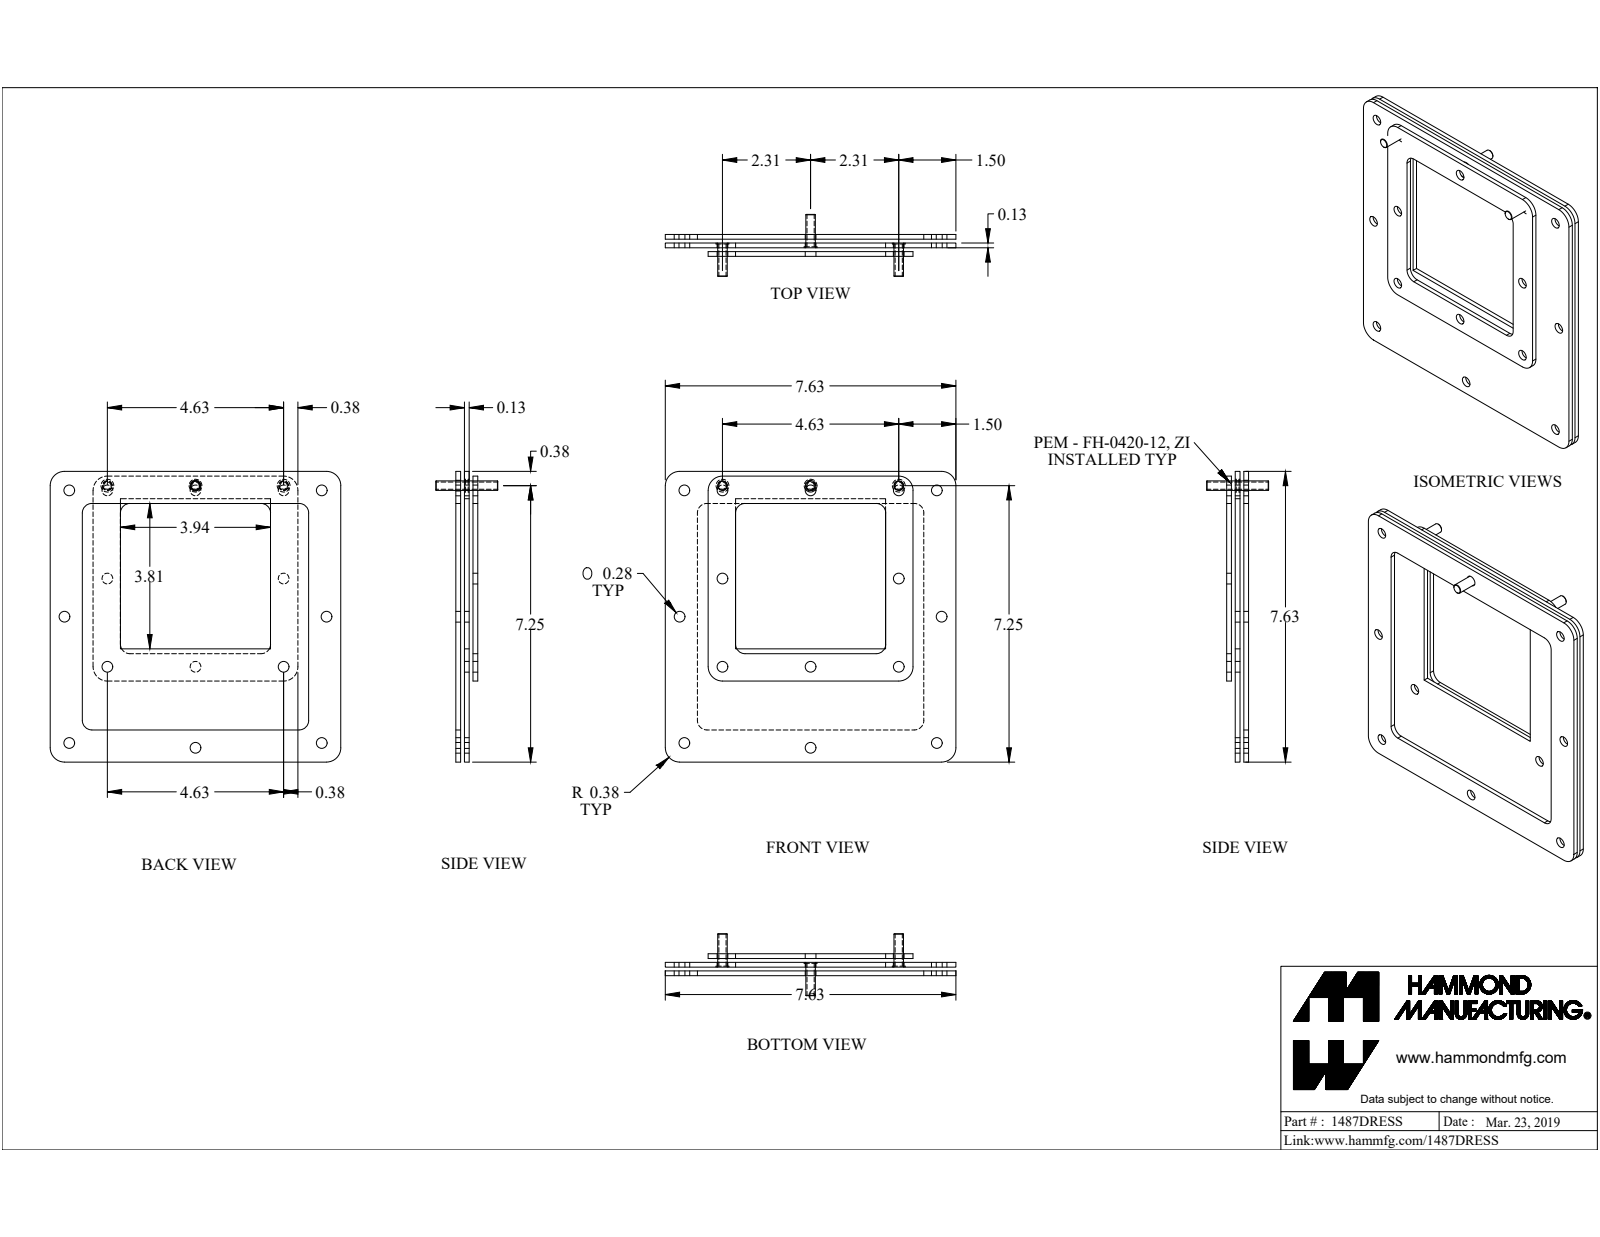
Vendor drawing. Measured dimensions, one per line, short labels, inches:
name: 1487DRESS
written by: SolidWorks 2019 (CONFIG_CONTROL_DESIGN)
unit: in
bodies: 12 solids, 270 faces (153 planar, 98 cylindrical, 19 other)
size: 7.625 × 7.625 × 1.625
volume: 9.929 in³; area: 181 in²
holes: 16× ⌀0.281, 3× ⌀0.249, 2× ⌀0.196, 2× ⌀0.258, 2× ⌀0.35
bosses: 5× ⌀0.25, 3× ⌀0.337, 2× ⌀0.5
rounds: 12× R0.02, 8× R0.25, 8× R0.375
face distances: 0.125, 0.225, 0.1, 0.35, 0.125, 0.35, 0.45, 0.325, 0.575, 0.225
hole spacings: 2.313, 7.519, 3.315, 5.171, 4.625, 5.283, 4.861, 0.125
